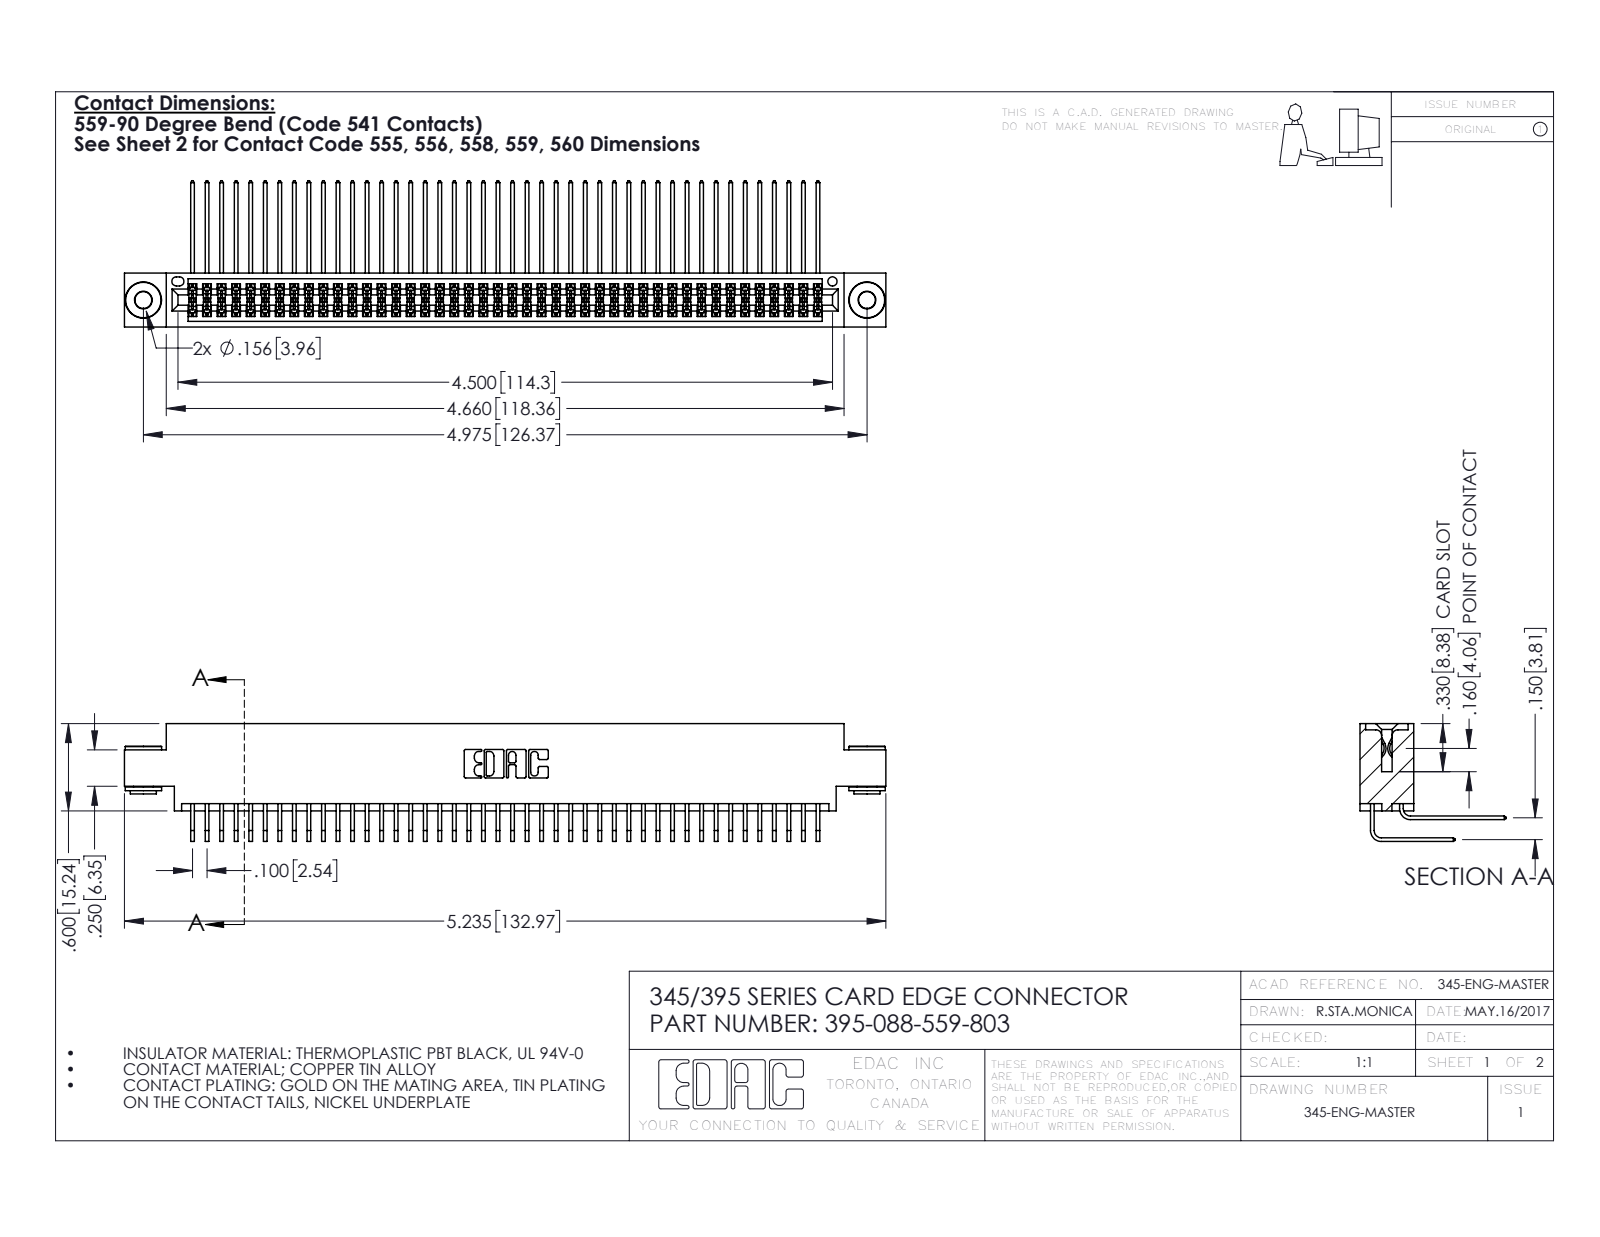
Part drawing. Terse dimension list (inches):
name: 345-292-001_559 Tail - 2; 345-250-002_345-250-002-102; 345-292-001_558 559 Tail - 1; 395-088-559-803 (+1 more)
written by: SolidWorks 2016 (CONFIG_CONTROL_DESIGN)
unit: in
bodies: 91 solids, 4744 faces (3174 planar, 1562 cylindrical, 8 other)
size: 5.235 × 1.005 × 0.809
volume: 0.815 in³; area: 34.88 in²
holes: 2× ⌀0.116, 2× ⌀0.156, 1× ⌀0.064
bosses: 2× ⌀0.25, 2× ⌀0.18, 2× ⌀0.136
rounds: 133× R0.006, 22× R0.01, 6× R0.007, 6× R0.031, 3× R0.026, 2× R0.014, 2× R0.019, 2× R0.022
face distances: 0.072, 0.298, 0.37, 0.2, 0.098, 0.272, 0.025, 0.175, 0.225, 0.15
hole spacings: 0.27, 4.739, 4.975
